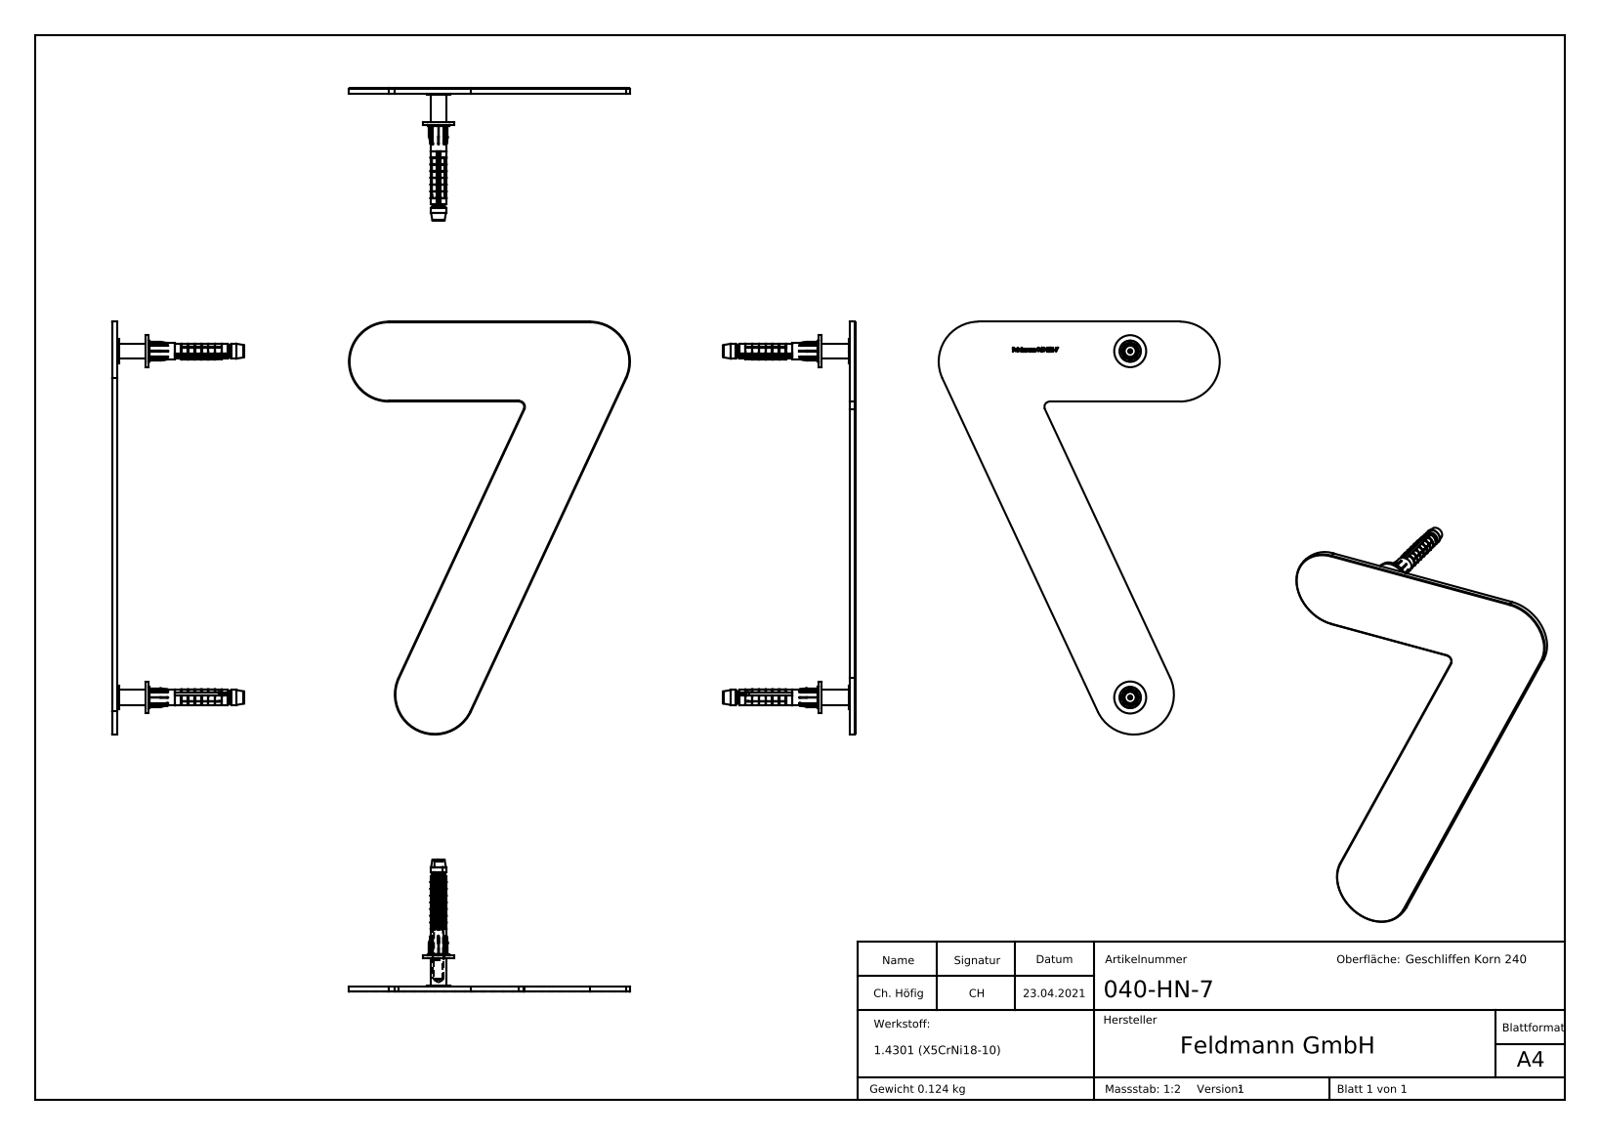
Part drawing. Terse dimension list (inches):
name: 040-HN-X Teil1_040-HN-7 Teil1; 040-HN-X Teil4; 040-HN-X Teil2_040-HN-X Teil2; 040-HN-7 (+5 more)
written by: SolidWorks 2018 (CONFIG_CONTROL_DESIGN)
unit: in
bodies: 7 solids, 1547 faces (361 planar, 388 cylindrical, 798 other)
size: 393.701 × 205.411 × 181.413
volume: 1.016 in³; area: 29.96 in²
holes: 2× ⌀0.13, 2× ⌀0.169
bosses: 2× ⌀0.472, 2× ⌀0.354, 2× ⌀0.315, 2× ⌀0.236, 2× ⌀0.228, 2× ⌀0.22, 2× ⌀0.181, 2× ⌀0.157
rounds: 22× R0.004, 4× R0.01, 3× R0.591, 2× R0.138, 1× R0.079
face distances: 0.079, 0.457, 0.535, 0.043, 0.413, 0.492, 1.179, 0.039, 0.02, 0.098
hole spacings: 5.118
